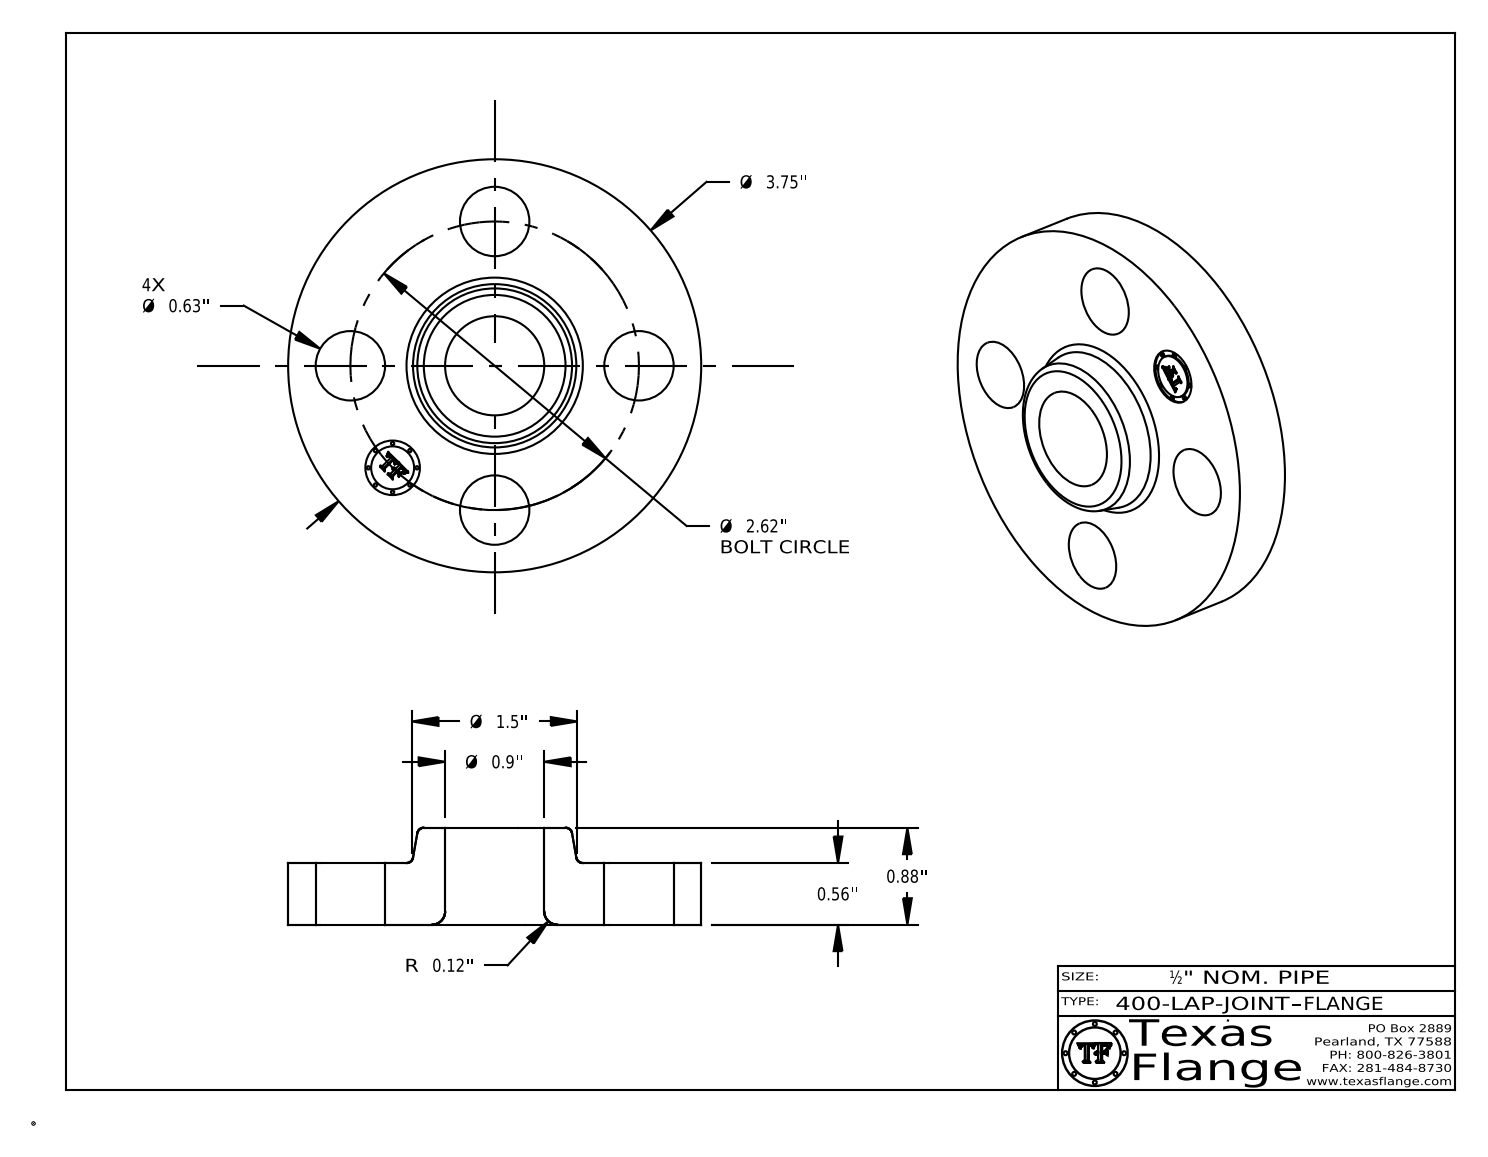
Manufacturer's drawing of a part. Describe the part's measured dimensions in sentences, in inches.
The part is named "400-LAP-JOINT FLANGE". Its 3-D file was written by "CATIA V5 STEP AP214 (AUTOMOTIVE_DESIGN)". It is 1 solid with 408 faces: 368 planar, 32 cylindrical and 8 other. Overall it measures 3.75 by 3.75 by 0.88 inches. Its volume is 5.441 cubic inches and its surface area 32.86 square inches. Round holes: 4 of diameter 0.63, 1 of diameter 0.495, 1 of diameter 0.9. Round bosses or shafts: 8 of diameter 0.03, 1 of diameter 3.75, 1 of diameter 0.39. The main face-to-face distances are 0.56, 0.88, 0.32, 0.545, 0.015, 0.335, 0.148, 0.144, 0.027, 0.096. The hole center spacings are 1.31, 1.852, 1.003, 2.42, 2.62, 1.31.
